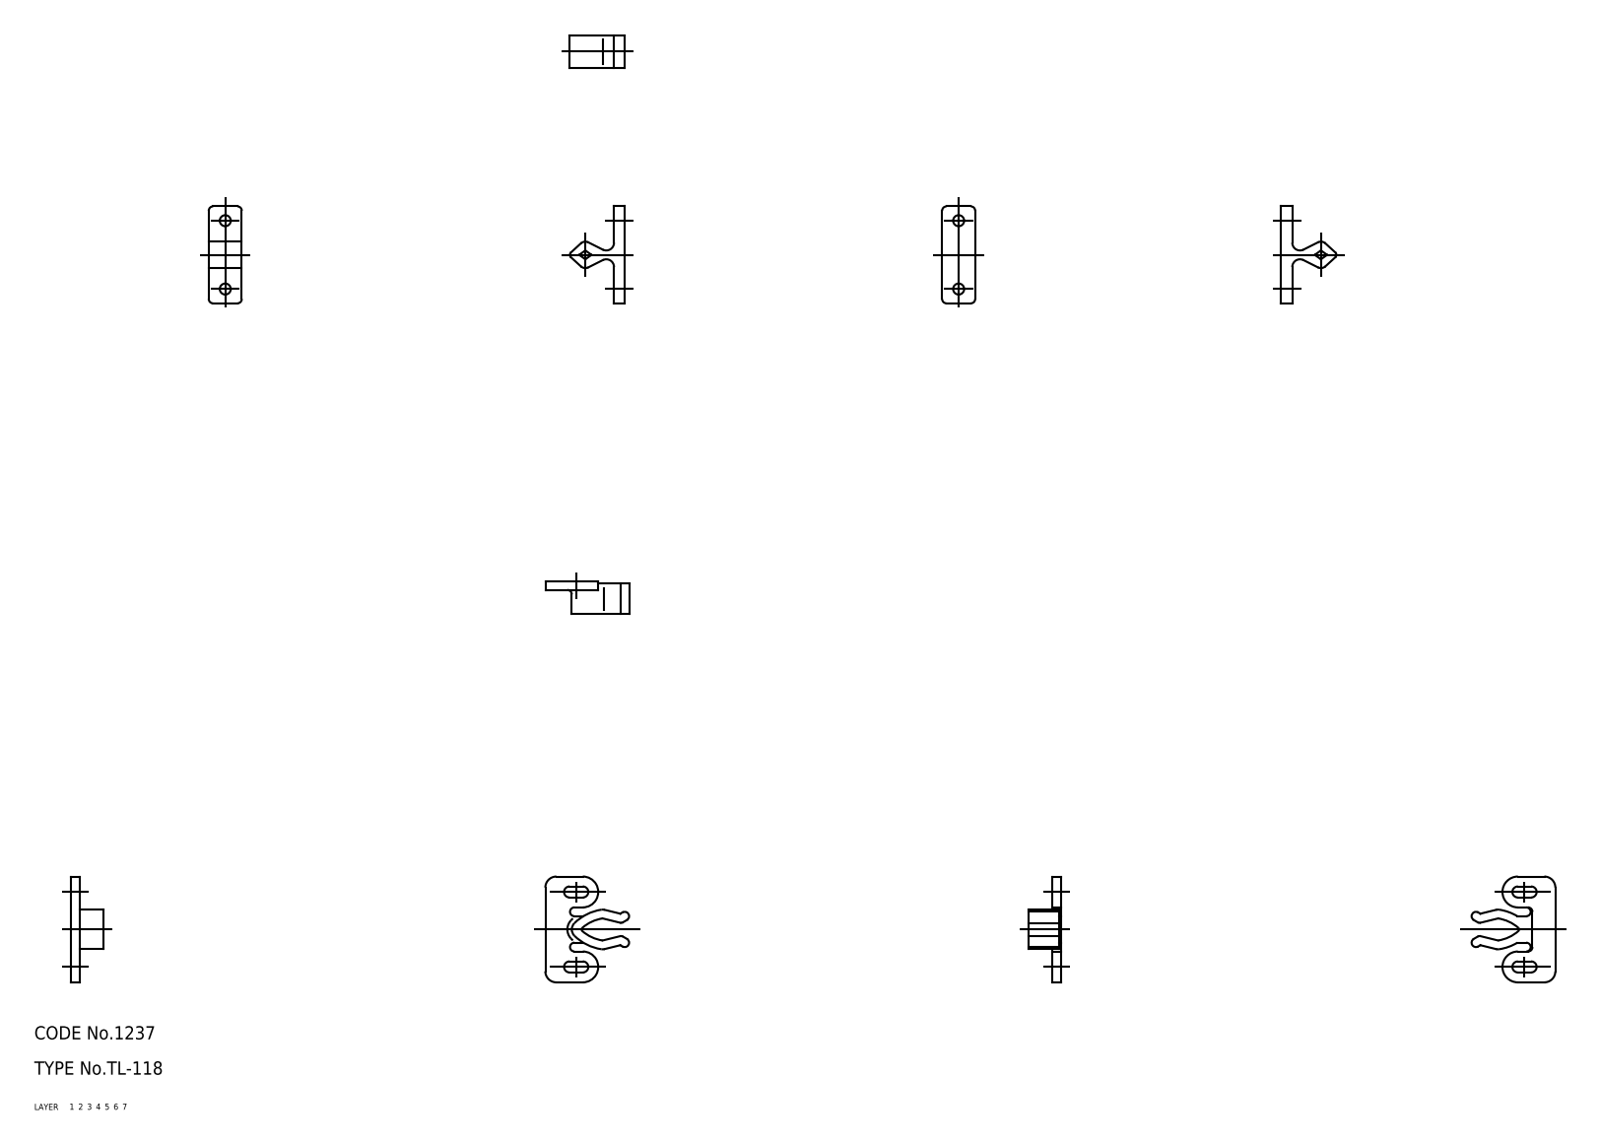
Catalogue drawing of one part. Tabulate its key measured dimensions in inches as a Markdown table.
| quantity | value |
| --- | --- |
| part name | keeper; base; TL_118_10617_36 |
| STEP written by | CADfix (AUTOMOTIVE_DESIGN) |
| units | inches |
| bodies | 2 solids, 79 faces (0 planar, 0 cylindrical, 79 other) |
| overall size | 1.634 × 0.945 × 0.295 |
| volume | 0.085 in³ |
| surface area | 2.85 in² |
